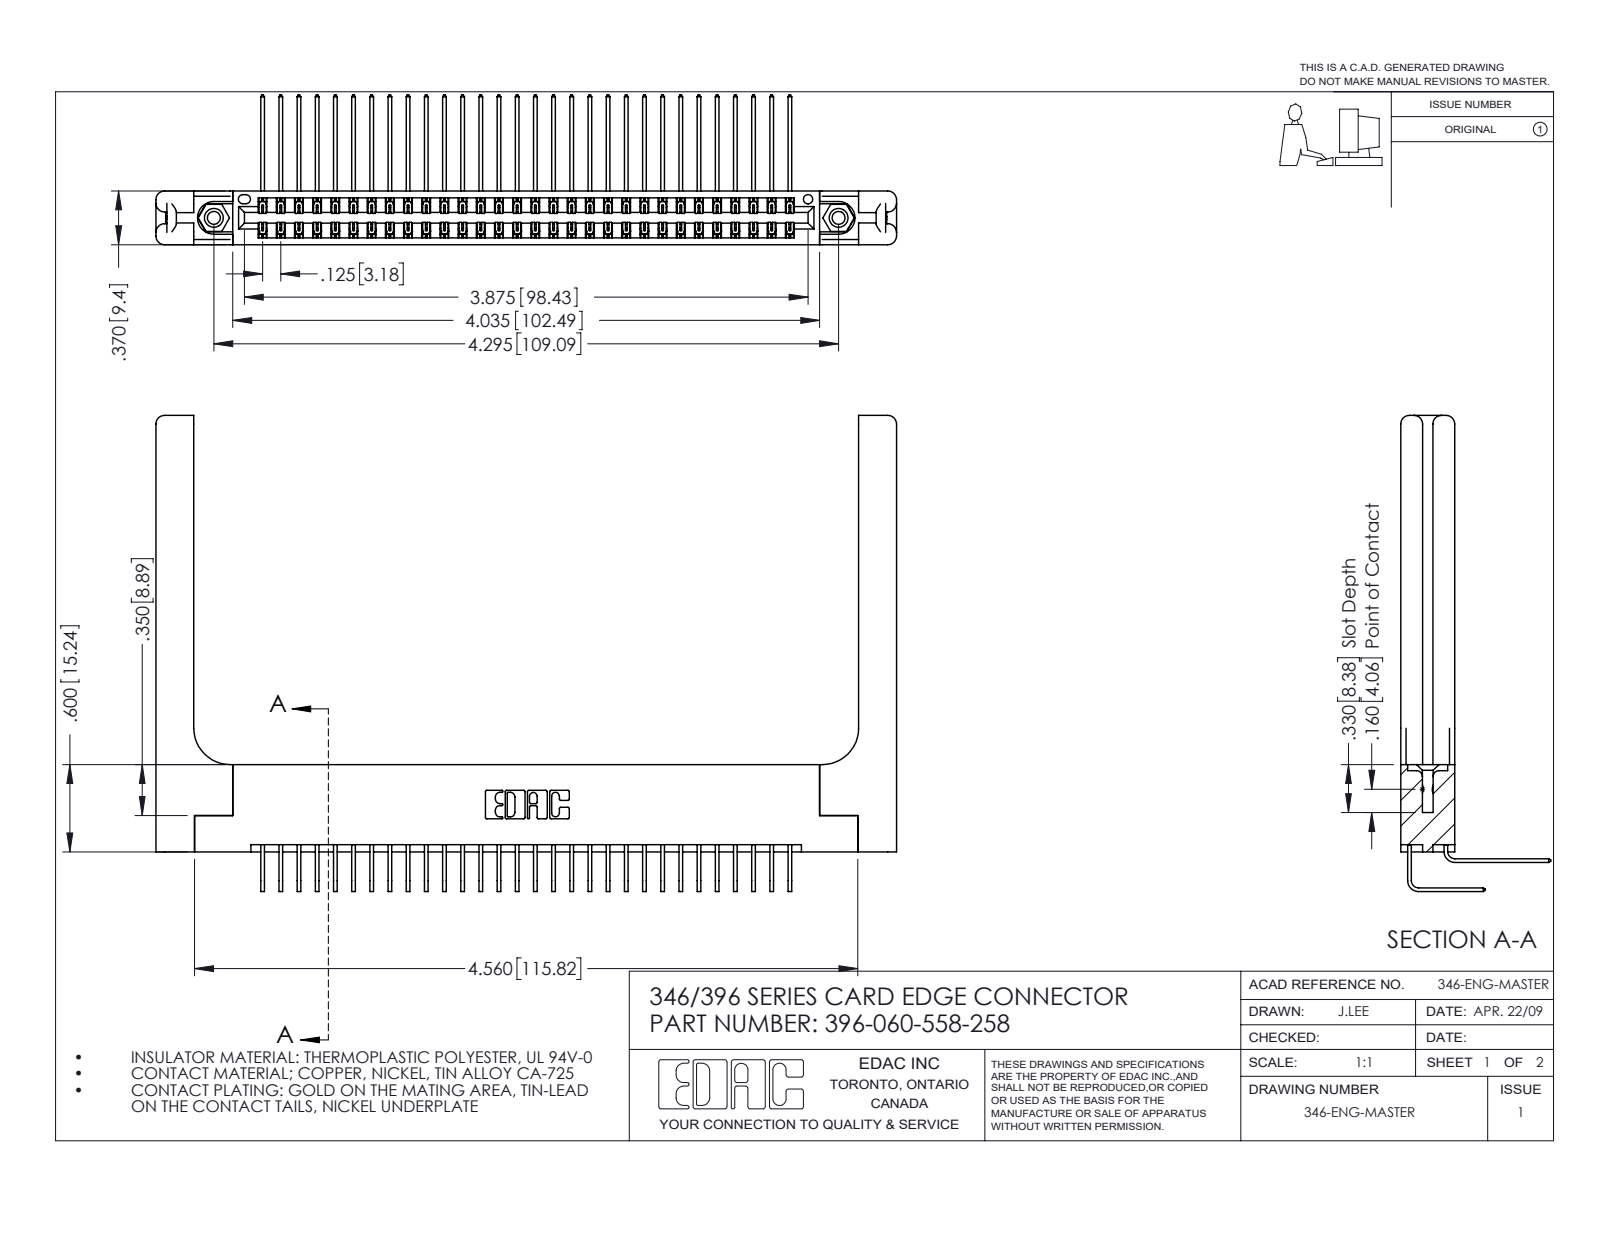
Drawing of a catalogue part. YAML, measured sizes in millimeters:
part_name: "346-220-058_345-220-058; 345-292-001_558 559 Tail - 1; 346 Part_Flush Mounting Lugs - 0.156 Dia-TH; 345-292-001_558 Tail - 2 (+2 more)"
step_written_by: "SolidWorks 2016 (CONFIG_CONTROL_DESIGN)"
units: millimeters
bodies: {solids: 65, faces: 3618, planar: 2444, cylindrical: 1114, other: 60}
overall_size: [129.3, 83.1, 26.2]
volume: 20350
surface_area: 24120
round_holes:
  - {diameter: 2.3, count: 2}
  - {diameter: 3.2, count: 2}
  - {diameter: 4, count: 2}
  - {diameter: 1.6, count: 1}
round_bosses_or_shafts:
  - {diameter: 3.9, count: 2}
partial_cylinders:
  - {radius: 0.2, count: 90}
  - {radius: 0.3, count: 22}
  - {radius: 1.5, count: 16}
  - {radius: 0.2, count: 6}
  - {radius: 0.8, count: 6}
  - {radius: 0.7, count: 3}
  - {radius: 0.4, count: 2}
  - {radius: 0.6, count: 2}
face_to_face_distances: [8.2, 9.4, 1.2, 1.8, 0.6, 7.6, 3.8, 3.8, 6.4, 7]
hole_center_spacings: [6.2, 103.8, 109.1]
